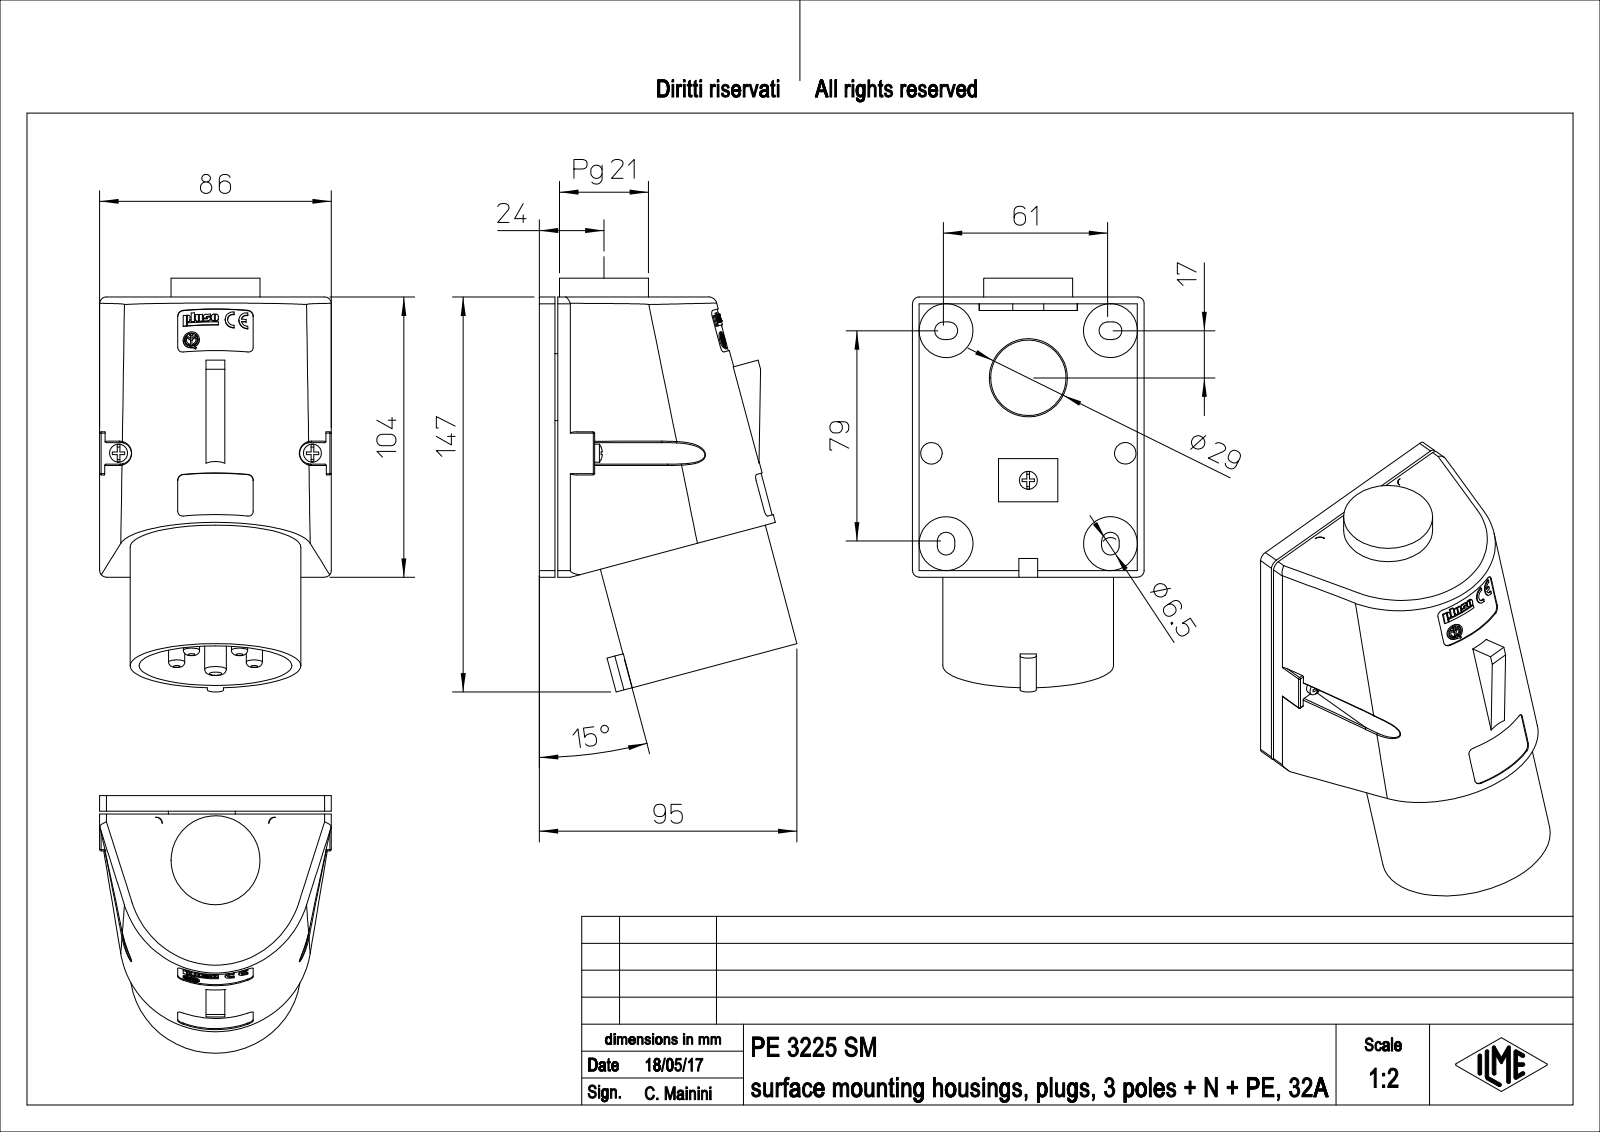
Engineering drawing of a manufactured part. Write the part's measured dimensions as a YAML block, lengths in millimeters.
part_name: "PE_3225_SM"
step_written_by: "PTC Creo Elements/Direct Modeling 19.0E 27-Jun-2016 (C) Parametric Technology GmbH (AUTOMOTIVE_DESIGN)"
units: millimeters
bodies: {solids: 1, faces: 1055, planar: 668, cylindrical: 220, other: 167}
overall_size: [153.55, 95.62, 86]
volume: 518948
surface_area: 96274
round_holes:
  - {diameter: 6.1, count: 4}
  - {diameter: 2.8, count: 2}
  - {diameter: 3.2, count: 2}
  - {diameter: 4, count: 2}
  - {diameter: 4.5, count: 2}
  - {diameter: 4.2, count: 1}
  - {diameter: 5.04, count: 1}
  - {diameter: 27.54, count: 1}
  - {diameter: 29, count: 1}
  - {diameter: 32, count: 1}
  - {diameter: 56.7, count: 1}
round_bosses_or_shafts:
  - {diameter: 6.7, count: 5}
  - {diameter: 6, count: 5}
  - {diameter: 20, count: 4}
  - {diameter: 8, count: 3}
  - {diameter: 3, count: 2}
  - {diameter: 63.4, count: 1}
  - {diameter: 33, count: 1}
  - {diameter: 24.84, count: 1}
partial_cylinders:
  - {radius: 0.5, count: 20}
  - {radius: 0.17, count: 11}
  - {radius: 2, count: 10}
  - {radius: 0.86, count: 9}
  - {radius: 3.25, count: 8}
  - {radius: 2.5, count: 6}
  - {radius: 0.75, count: 4}
  - {radius: 4.5, count: 4}
face_to_face_distances: [1.07, 4.75, 5.82, 7, 1, 5.75, 6.82, 2.25, 2.5, 8]
hole_center_spacings: [15.15, 72, 17.81, 21.93, 24.8, 28.81, 37.36, 37.37]
